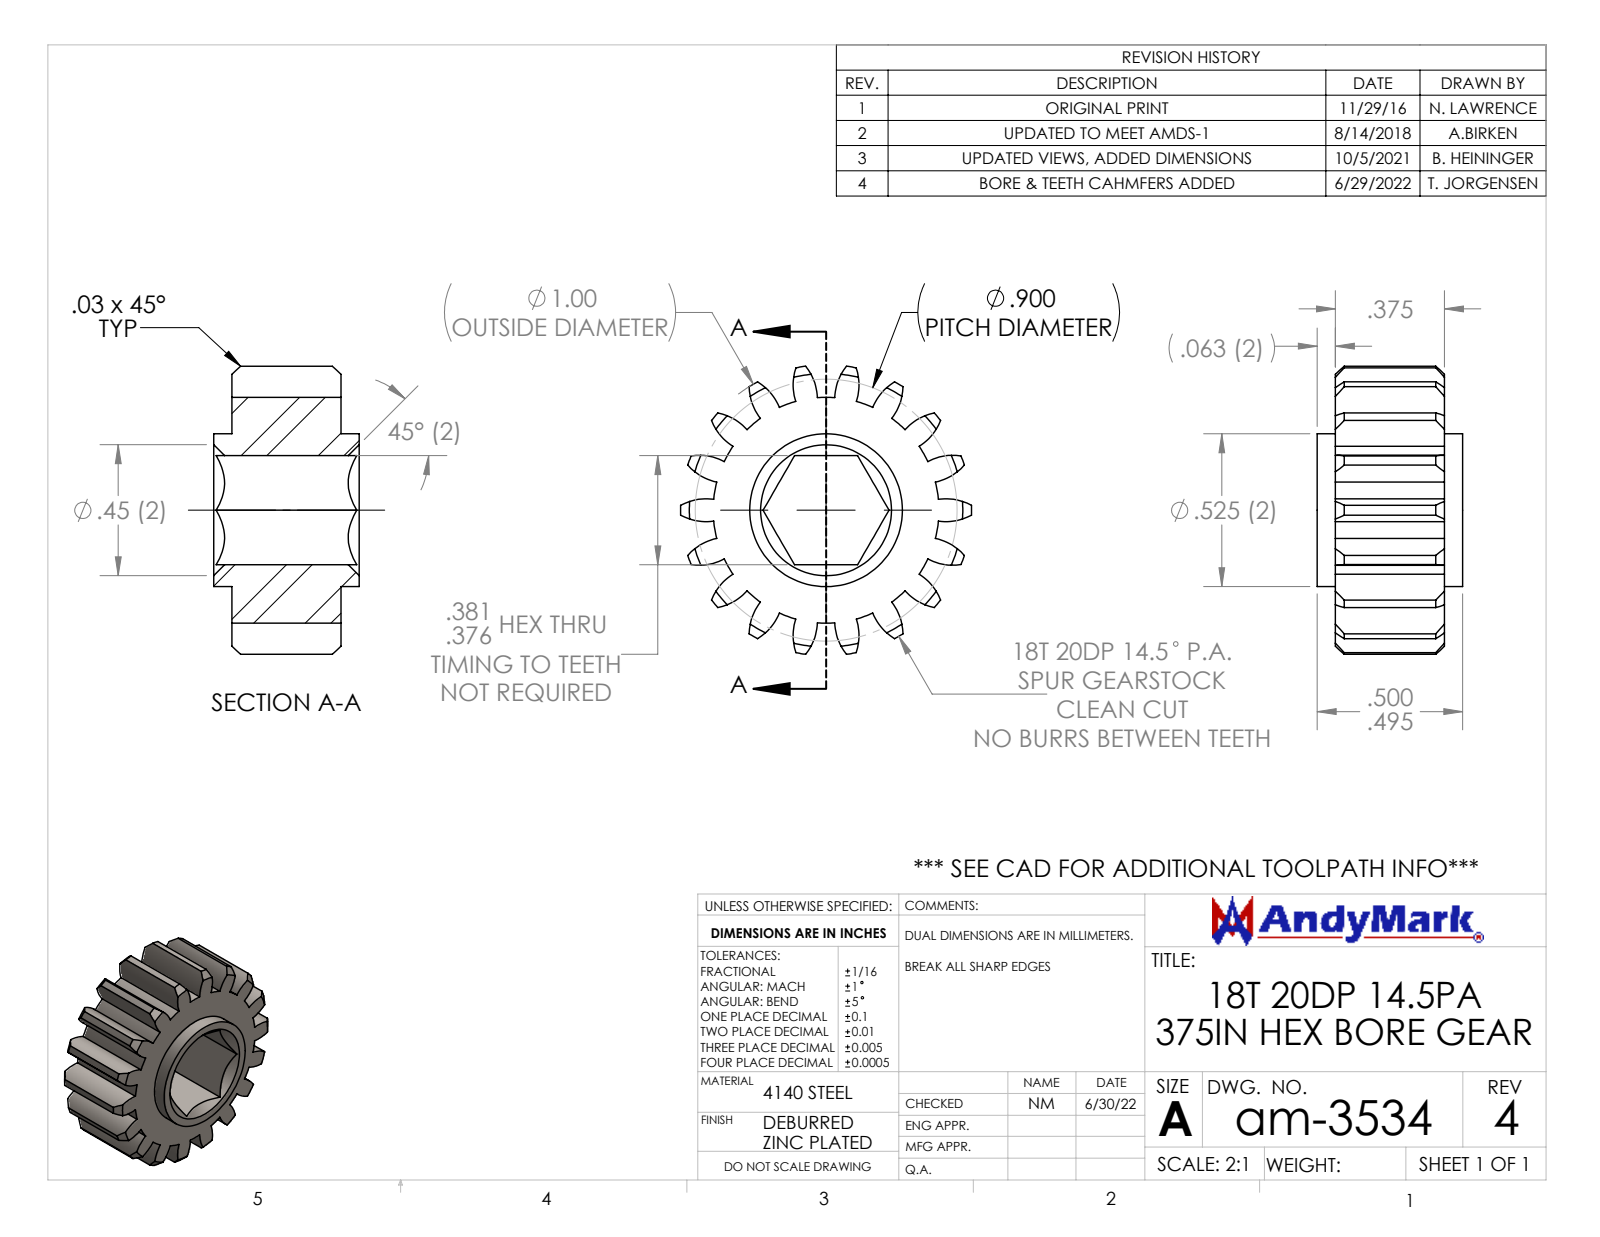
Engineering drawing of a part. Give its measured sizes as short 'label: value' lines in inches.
name: am-3534 18T 20DP 375hex 375 FW
written by: SolidWorks 2022 (CONFIG_CONTROL_DESIGN)
unit: in
bodies: 1 solid, 129 faces (10 planar, 79 cylindrical, 40 other)
size: 1 × 0.99 × 0.5
volume: 0.193 in³; area: 3.957 in²
bosses: 1× ⌀0.525
rounds: 36× R0.18, 1× R0.388, 1× R0.5
face distances: 0.375, 0.375, 0.063, 0.438, 0.5, 0.437, 0.062
